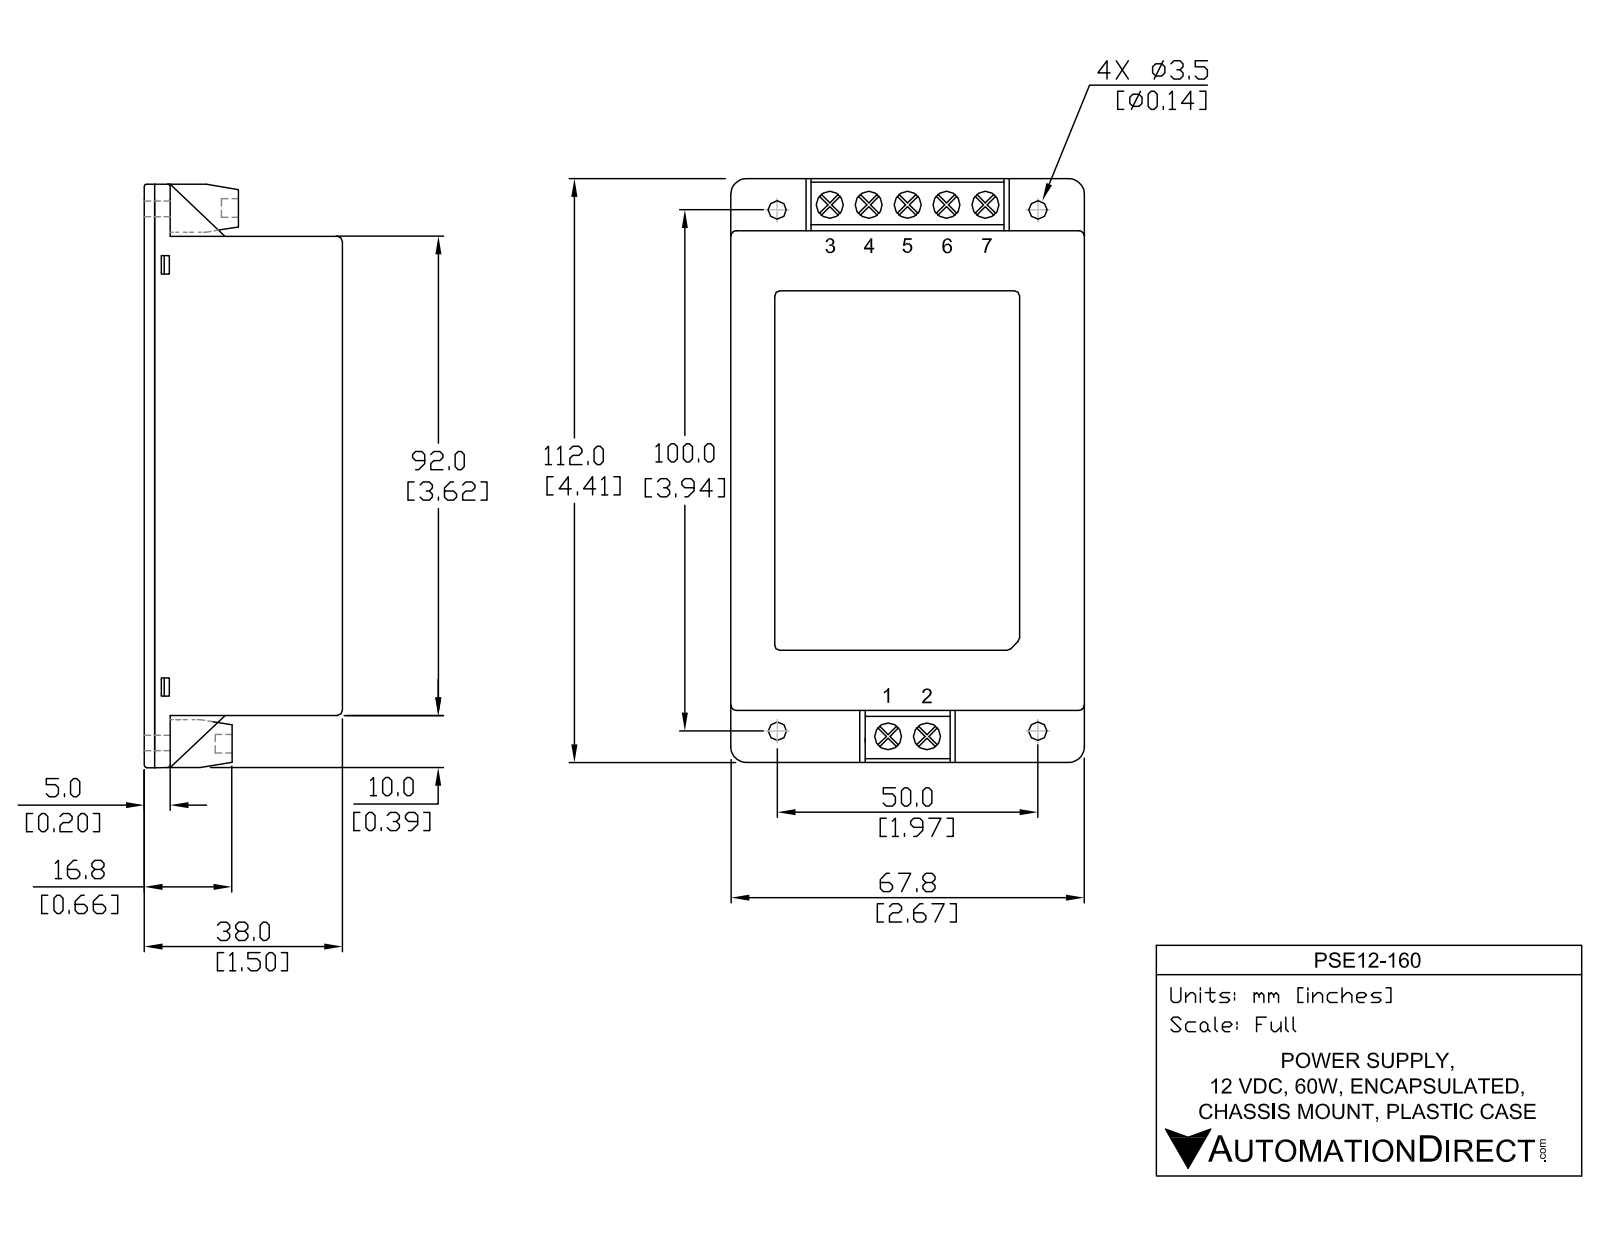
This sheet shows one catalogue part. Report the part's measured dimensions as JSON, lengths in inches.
{"part_name": "PSE12-160", "step_written_by": "SolidWorks 2011 (CONFIG_CONTROL_DESIGN)", "units": "inches", "bodies": {"solids": 2, "faces": 374, "planar": 246, "cylindrical": 62, "other": 66}, "overall_size": [4.41, 2.67, 1.5], "volume_in3": 15.18, "surface_area_in2": 69.77, "round_holes": [[0.2, 7], [0.14, 4]], "partial_cylinders_radius": [[0.03, 20], [0.125, 4]], "face_to_face_distances": [0.078, 0.08, 1.42, 2.67, 1.498, 1.418, 1.5, 1.422, 3.62, 0.015], "hole_center_spacings": [0.26, 0.52, 0.26, 0.856, 1.116, 1.97, 3.94, 4.015]}
